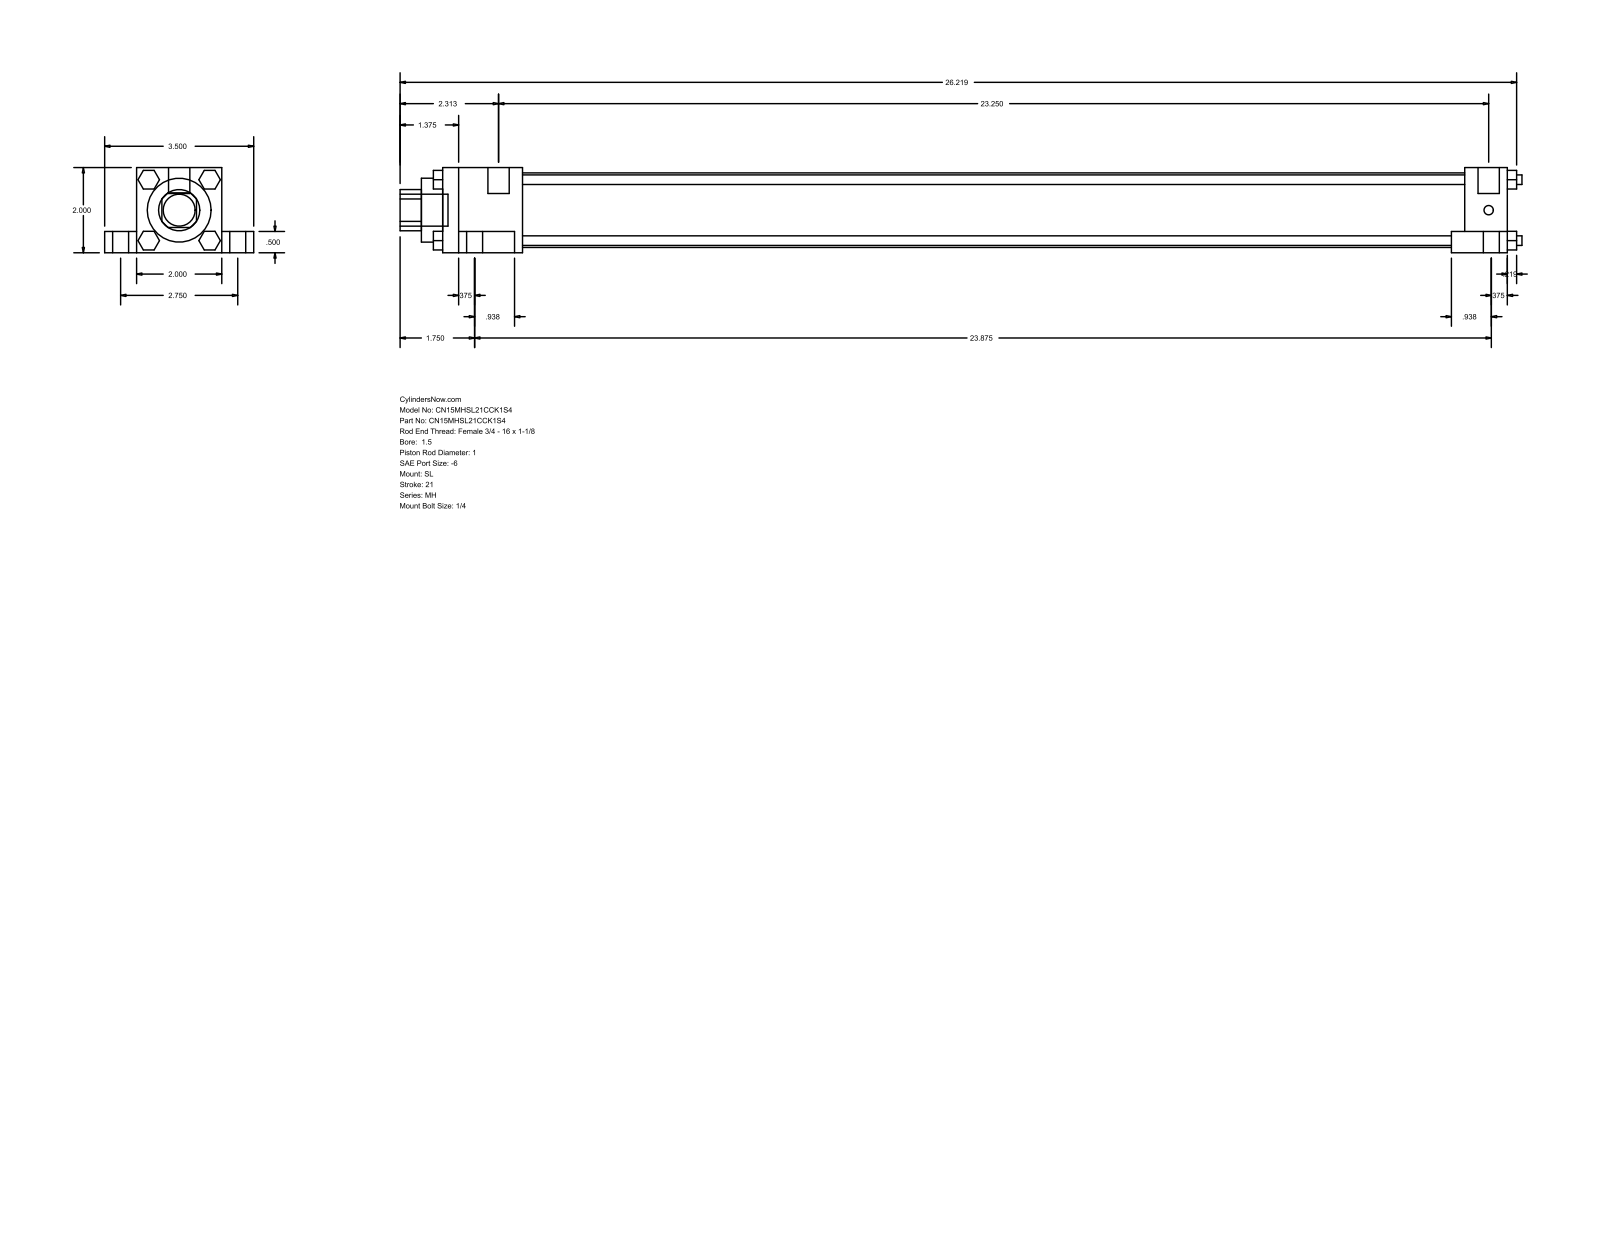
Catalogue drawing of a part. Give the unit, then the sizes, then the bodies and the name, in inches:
Units: inches
Overall size (bounding box): 26.344 × 3.5 × 2
Round holes (diameter × count): ⌀1 ×1, ⌀1.5 ×1, ⌀1.75 ×1
Round bosses / shafts (diameter × count): ⌀0.625 ×4, ⌀0.375 ×4, ⌀0.225 ×4, ⌀0.219 ×4, ⌀0.5 ×2, ⌀0.75 ×1
Partial cylindrical surfaces — rounded edges, fillets, slot ends (radius × count): R0.484 ×1
Main face-to-face distances: 2, 0.5, 1.5, 0.75, 2.75, 25, 1, 0.375, 1.313, 23.313
Bodies: 0 solids, 148 faces (112 planar, 36 cylindrical, 0 other)
Part name (STEP PRODUCT): MH_SL__0150_1
STEP written by: GSSL Pune (CONFIG_CONTROL_DESIGN)
